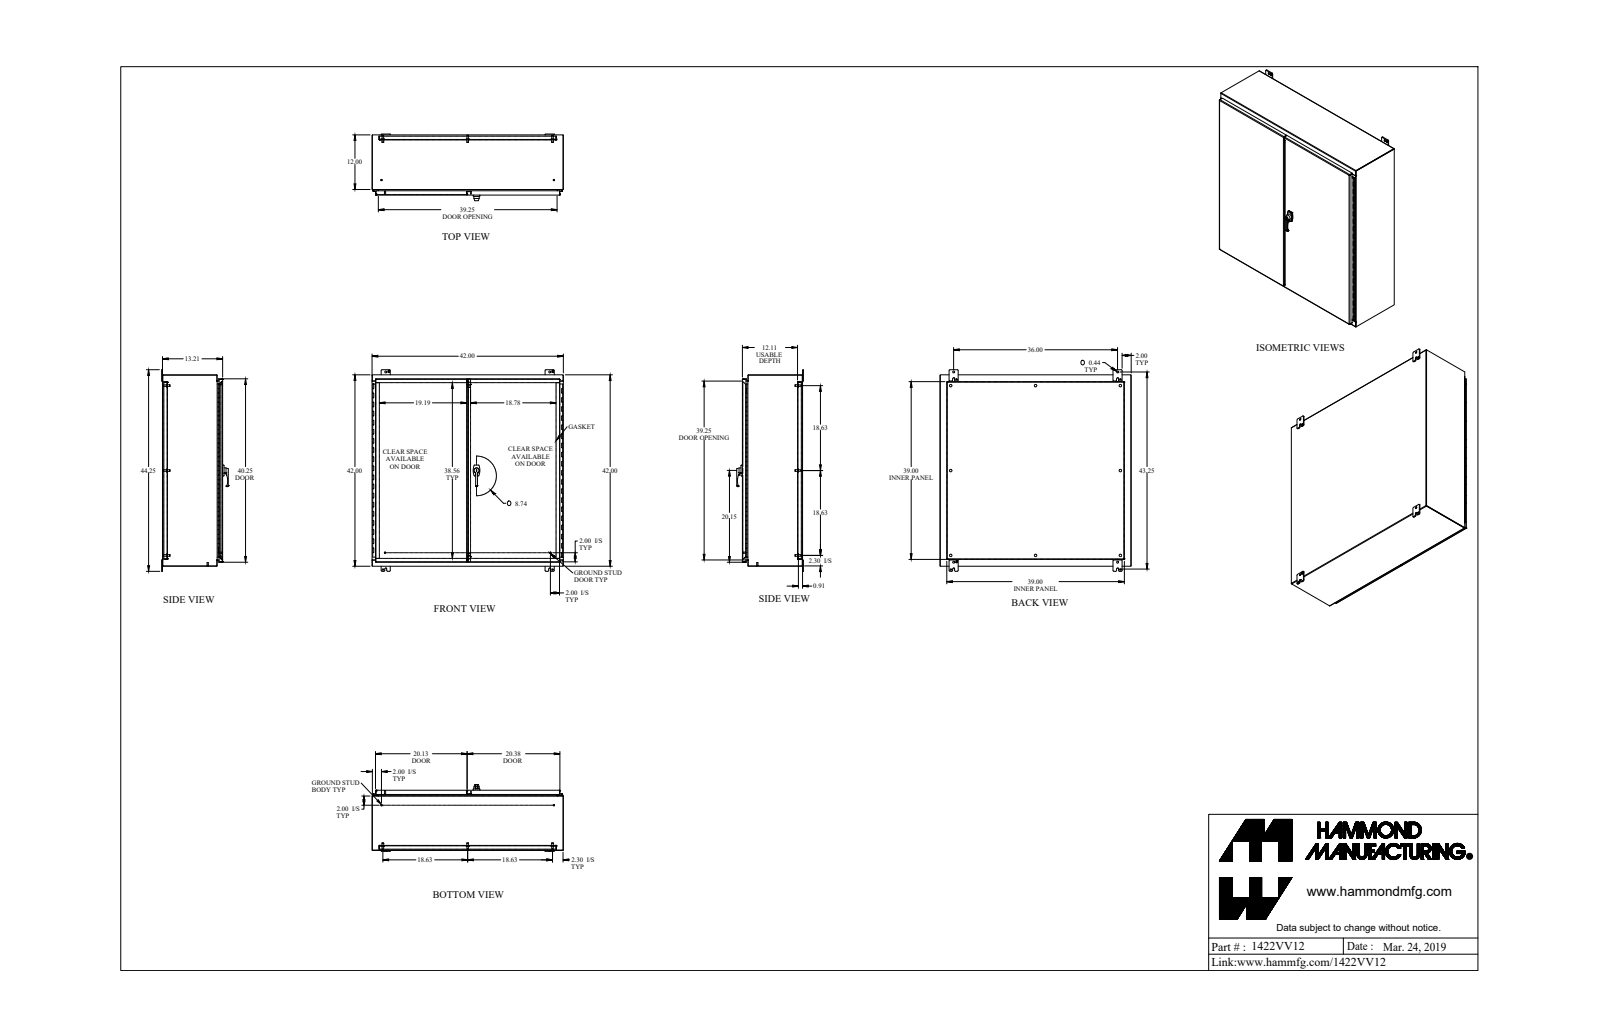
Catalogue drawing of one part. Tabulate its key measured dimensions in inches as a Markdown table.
| quantity | value |
| --- | --- |
| part name | 1422VV12 |
| STEP written by | SolidWorks 2019 (AUTOMOTIVE_DESIGN) |
| units | inches |
| bodies | 83 solids, 1789 faces (1134 planar, 531 cylindrical, 124 other) |
| overall size | 44.25 × 42 × 14.637 |
| volume | 713 in³ |
| surface area | 16 969 in² |
| round holes (diameter × count) | 0.304 × 14, 0.307 × 9, 0.445 × 8, 0.563 × 8, 0.218 × 4, 0.313 × 4, 0.437 × 4, 0.215 × 3, 0.11 × 2, 0.127 × 2, 0.156 × 2, 0.187 × 2 |
| round bosses / shafts (diameter × count) | 1 × 9, 0.65 × 8, 0.375 × 8, 0.33 × 8, 0.5 × 5, 0.313 × 4, 0.281 × 4, 0.25 × 4 |
| partial cylindrical surfaces (radius × count) | 0.188 × 35, 0.048 × 22, 0.143 × 22, 0.05 × 16, 0.036 × 14, 0.108 × 14, 0.116 × 12, 0.062 × 8 |
| main face-to-face distances | 0.072, 41.928, 13.043, 13.115, 0.095, 0.095, 0.937, 13.138, 13.21, 12.106 |
| hole center spacings | 6, 40.835, 12, 42.137, 18, 44.221, 40.392, 24 |
